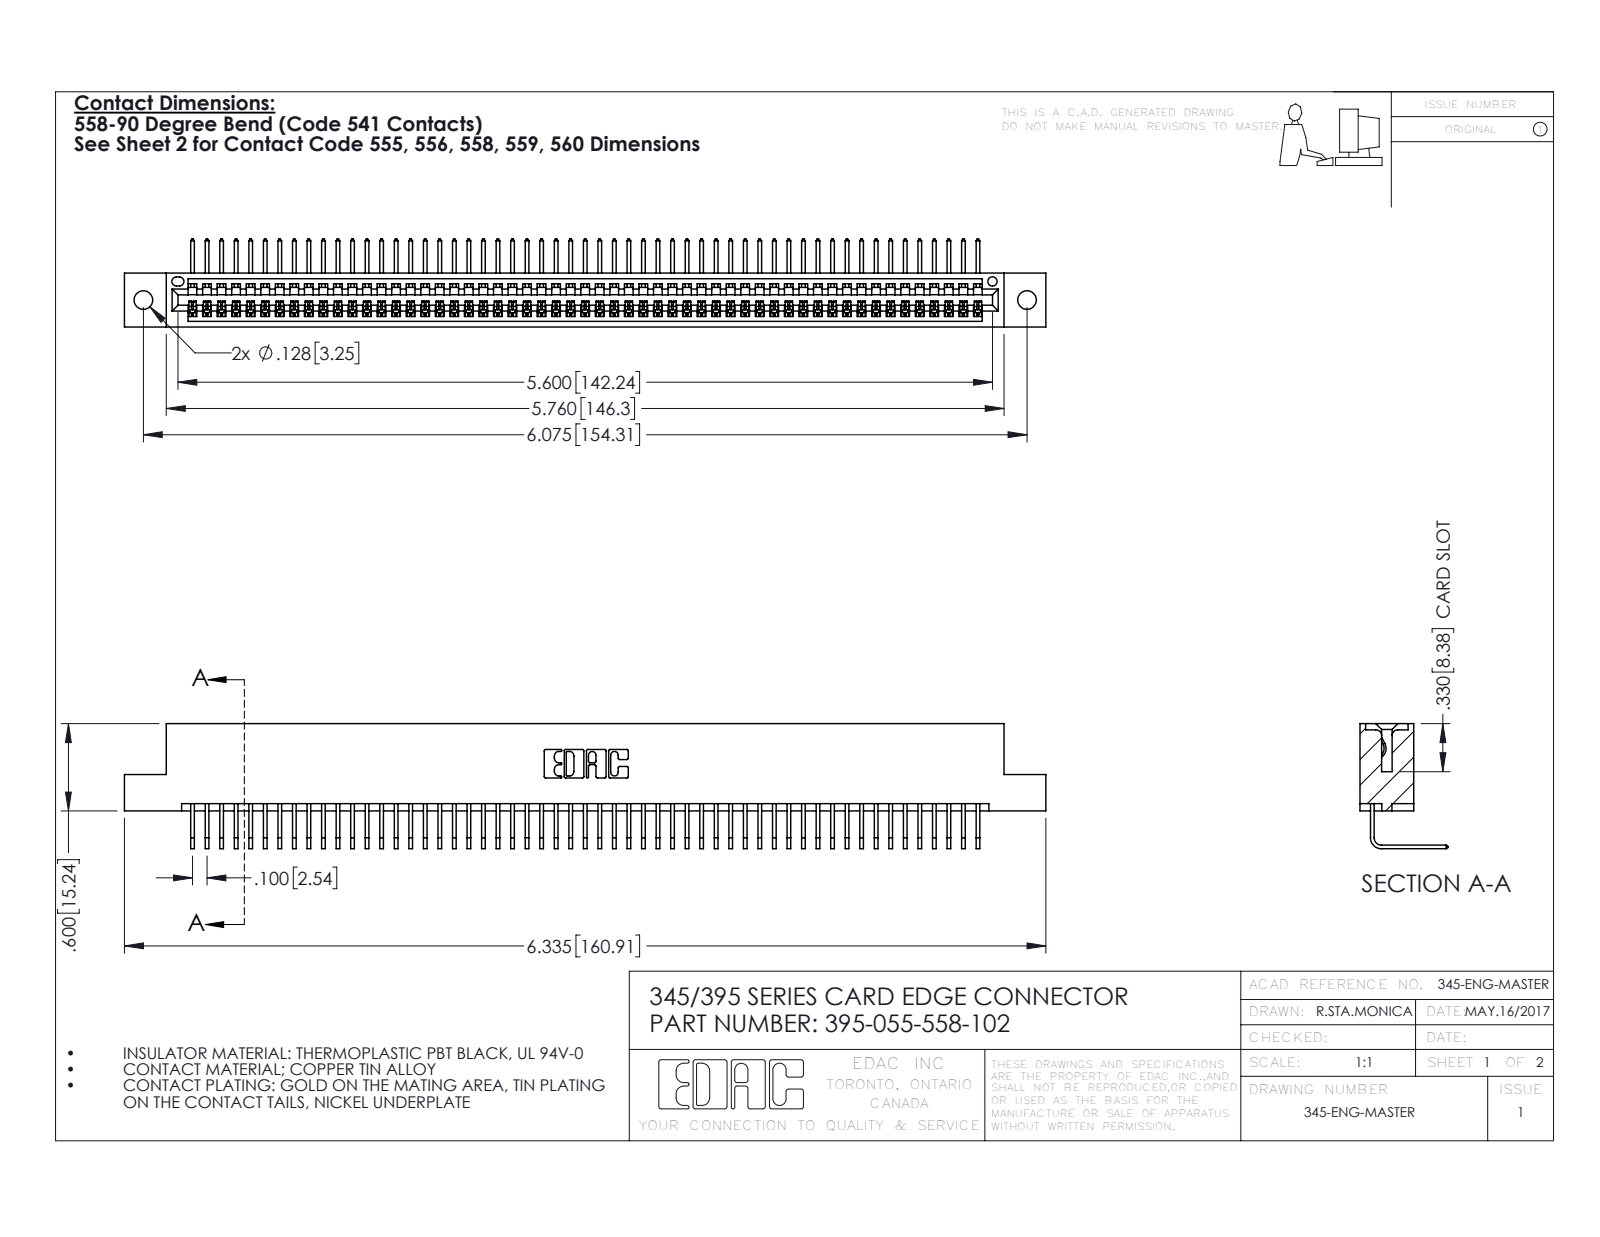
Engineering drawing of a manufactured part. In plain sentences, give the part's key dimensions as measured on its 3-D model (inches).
The part is named "345 Part_Flush Mounting Lugs - 0.128 Dia; 345-292-001_558 Tail - 2; 395-055-558-102". Its 3-D file was written by "SolidWorks 2016 (CONFIG_CONTROL_DESIGN)". It is 56 solids with 3426 faces: 2390 planar, 1036 cylindrical and 0 other. Overall it measures 6.335 by 0.859 by 0.605 inches. Its volume is 0.948 cubic inches and its surface area 33.52 square inches. Round holes: 2 of diameter 0.128, 1 of diameter 0.064. Partial cylindrical surfaces (rounded edges, fillets, slot ends): 110 of radius 0.006, 22 of radius 0.01, 6 of radius 0.007, 6 of radius 0.031, 3 of radius 0.026, 2 of radius 0.031, 2 of radius 0.04, 1 of radius 0.014. The main face-to-face distances are 0.298, 0.072, 0.37, 0.2, 0.098, 0.272, 0.025, 0.225, 0.149, 0.072. The hole center spacings are 0.27, 5.839, 6.075.
